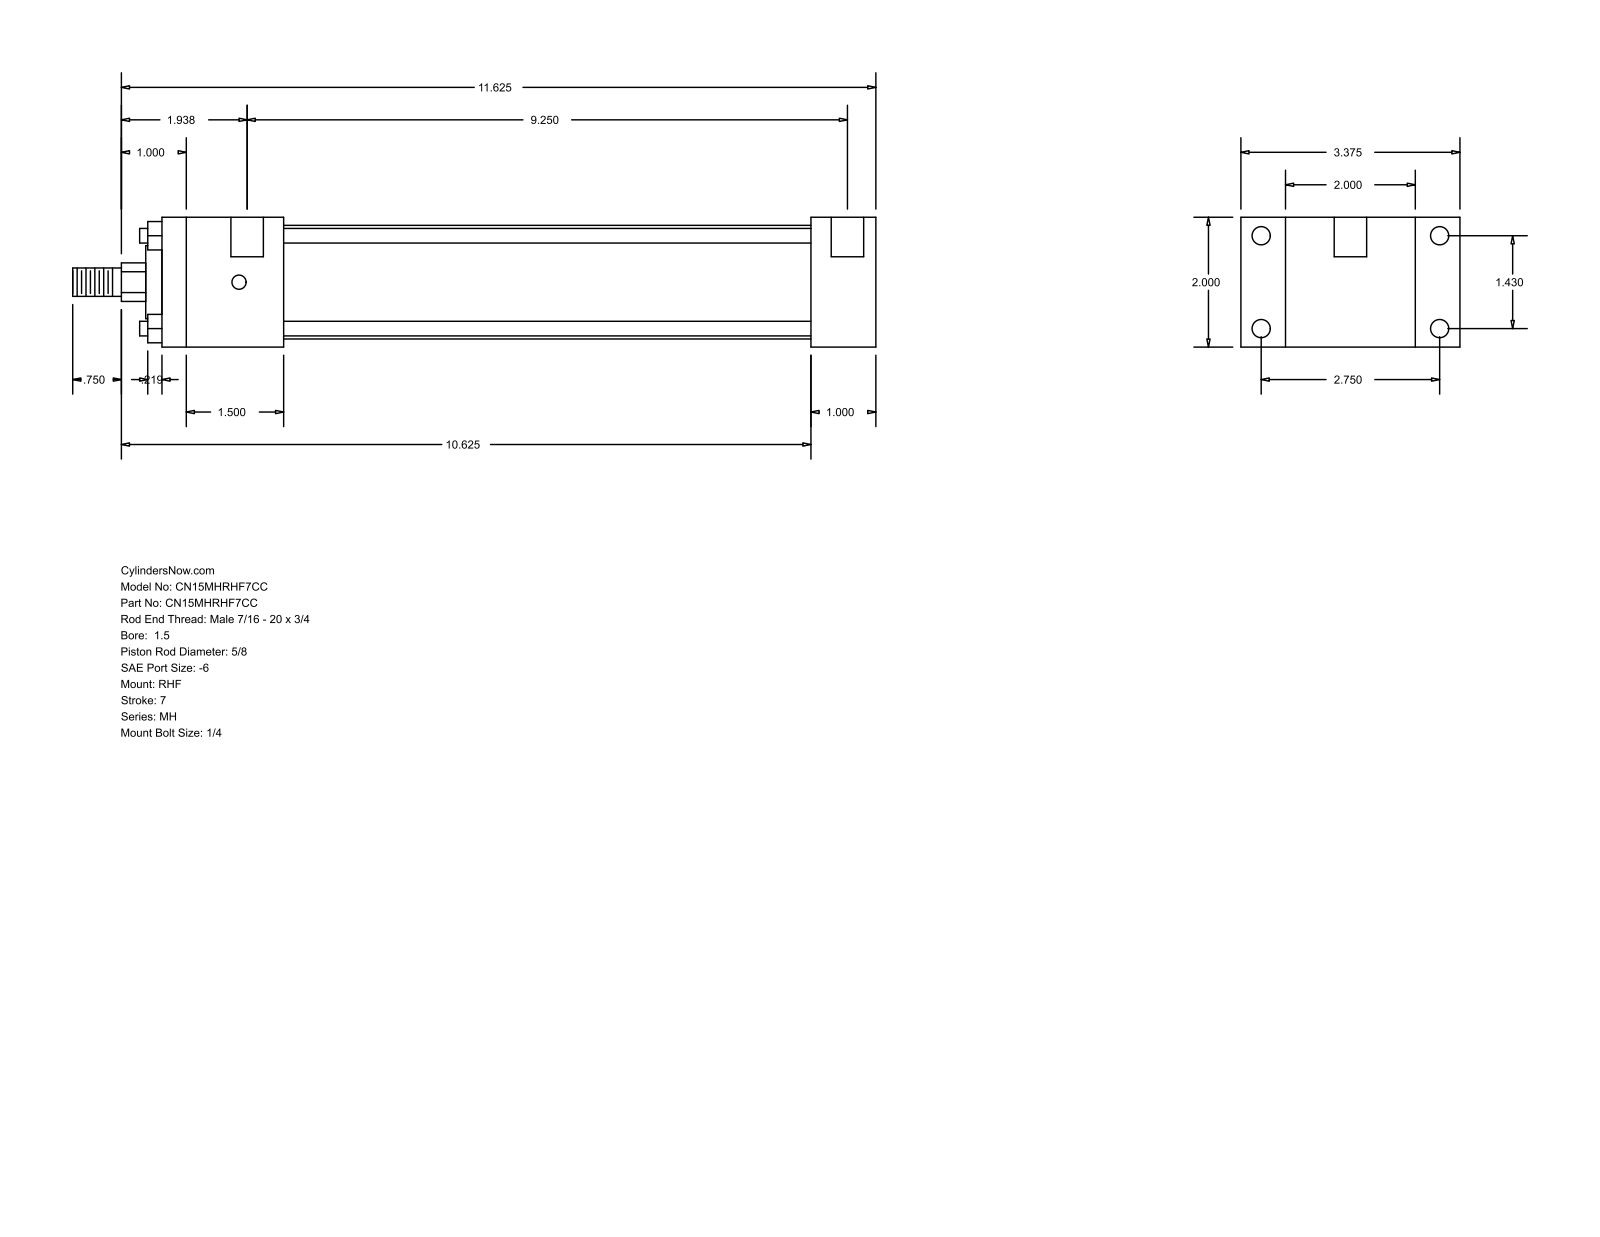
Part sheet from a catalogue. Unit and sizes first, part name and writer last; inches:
Units: inches
Overall size (bounding box): 12.375 × 3.375 × 2
Round holes (diameter × count): ⌀0.219 ×4, ⌀0.281 ×4, ⌀0.5 ×2
Round bosses / shafts (diameter × count): ⌀0.225 ×4, ⌀1.75 ×1, ⌀1.125 ×1, ⌀0.625 ×1, ⌀0.437 ×1
Partial cylindrical surfaces — rounded edges, fillets, slot ends (radius × count): R0.297 ×1
Main face-to-face distances: 2, 0.687, 2.687, 1, 10, 11, 3.375, 1.875, 8.125, 9.125
Hole centre spacings: 1.43, 2.75, 3.099, 9.375, 0.125, 9.25
Bodies: 0 solids, 88 faces (60 planar, 28 cylindrical, 0 other)
Part name (STEP PRODUCT): MH_RHF__0150_0.625
STEP written by: GSSL Pune (CONFIG_CONTROL_DESIGN)
